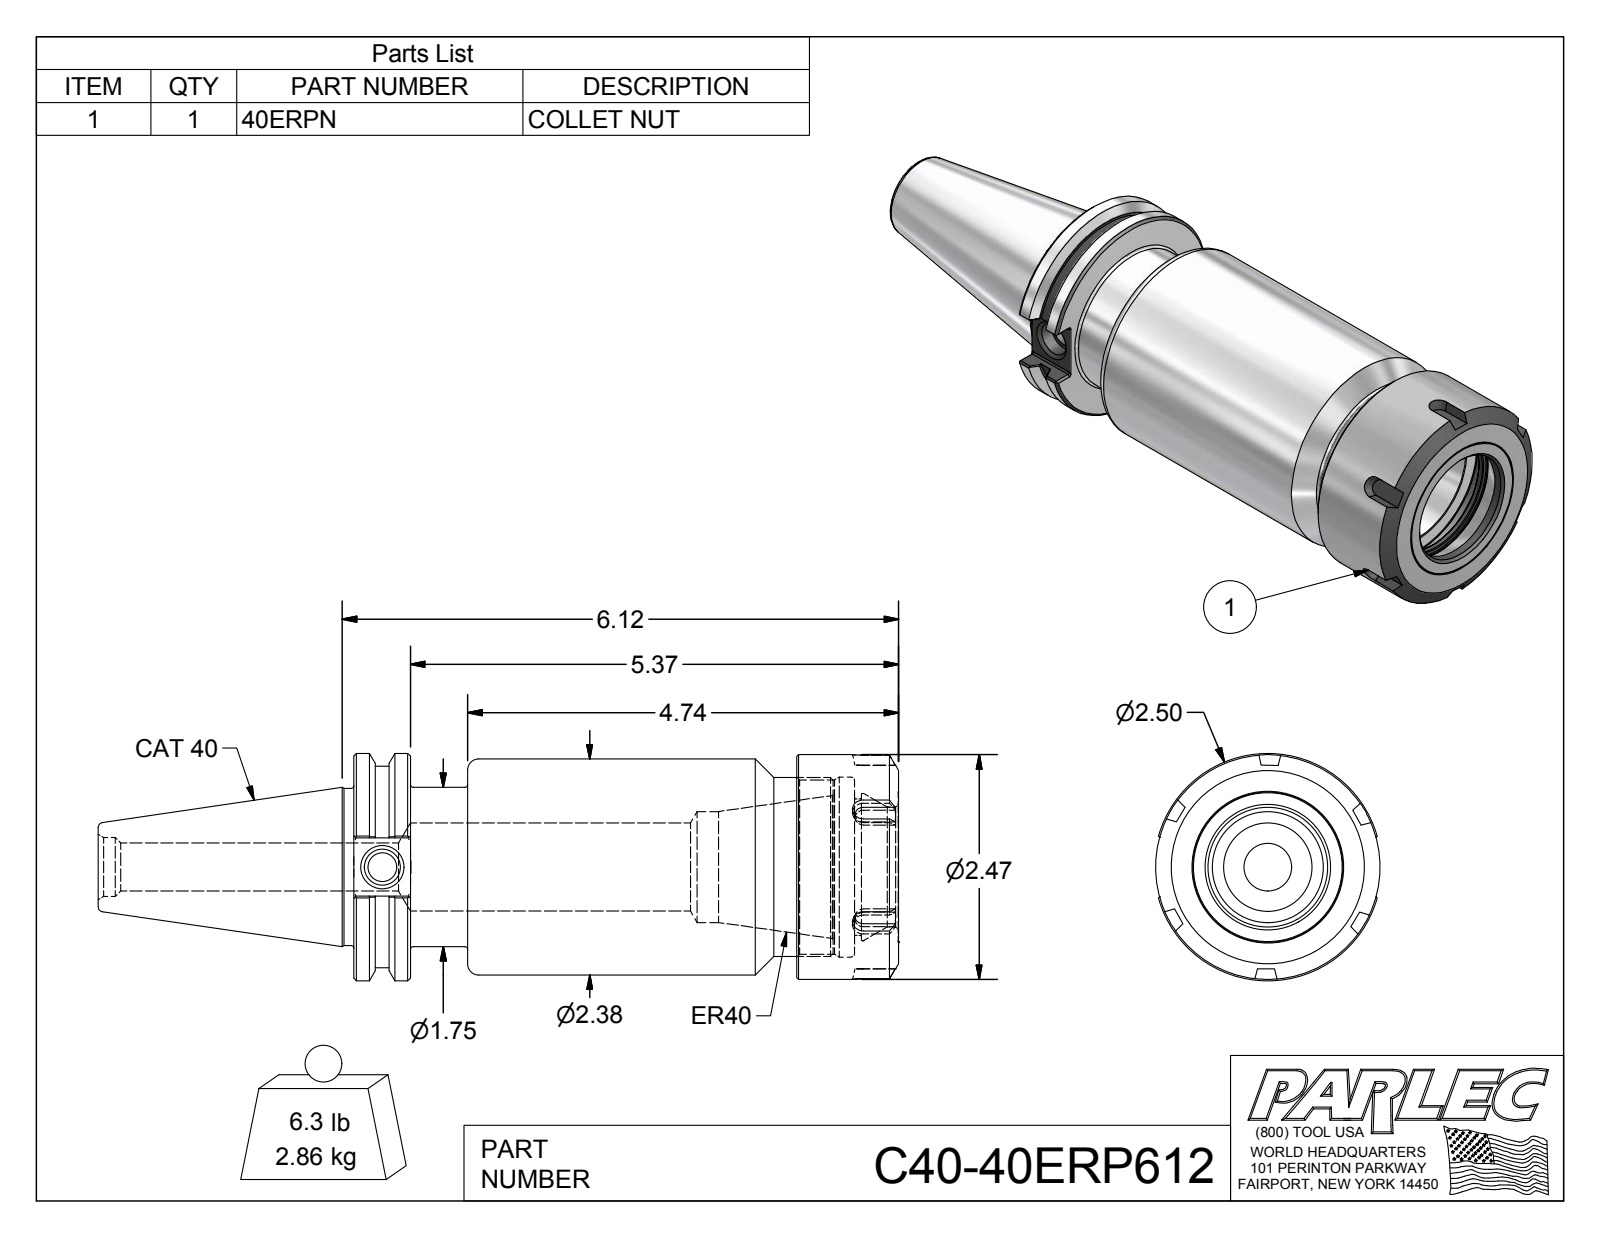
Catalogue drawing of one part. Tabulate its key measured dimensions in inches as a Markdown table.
| quantity | value |
| --- | --- |
| part name | C40-40ERP612; C40-40ER6-1; 40ERPN |
| STEP written by | Autodesk Inventor 2012 (AUTOMOTIVE_DESIGN) |
| units | inches |
| bodies | 2 solids, 141 faces (55 planar, 34 cylindrical, 52 other) |
| overall size | 8.807 × 2.5 × 2.47 |
| volume | 22.35 in³ |
| surface area | 102.7 in² |
| round holes (diameter × count) | 0.315 × 1, 0.399 × 1, 0.527 × 1, 0.648 × 1, 0.97 × 1, 1.22 × 1, 1.318 × 1, 1.5 × 1, 1.62 × 1, 1.916 × 1, 1.98 × 1 |
| round bosses / shafts (diameter × count) | 2.5 × 1, 2.47 × 1, 2.375 × 1, 2.219 × 1, 1.969 × 1, 1.75 × 1, 1.73 × 1 |
| partial cylindrical surfaces (radius × count) | 0.02 × 12 |
| main face-to-face distances | 5.995, 0.625, 5.37, 4.875, 4.25, 1.12, 5.511, 4.886, 0.636, 0.484 |
